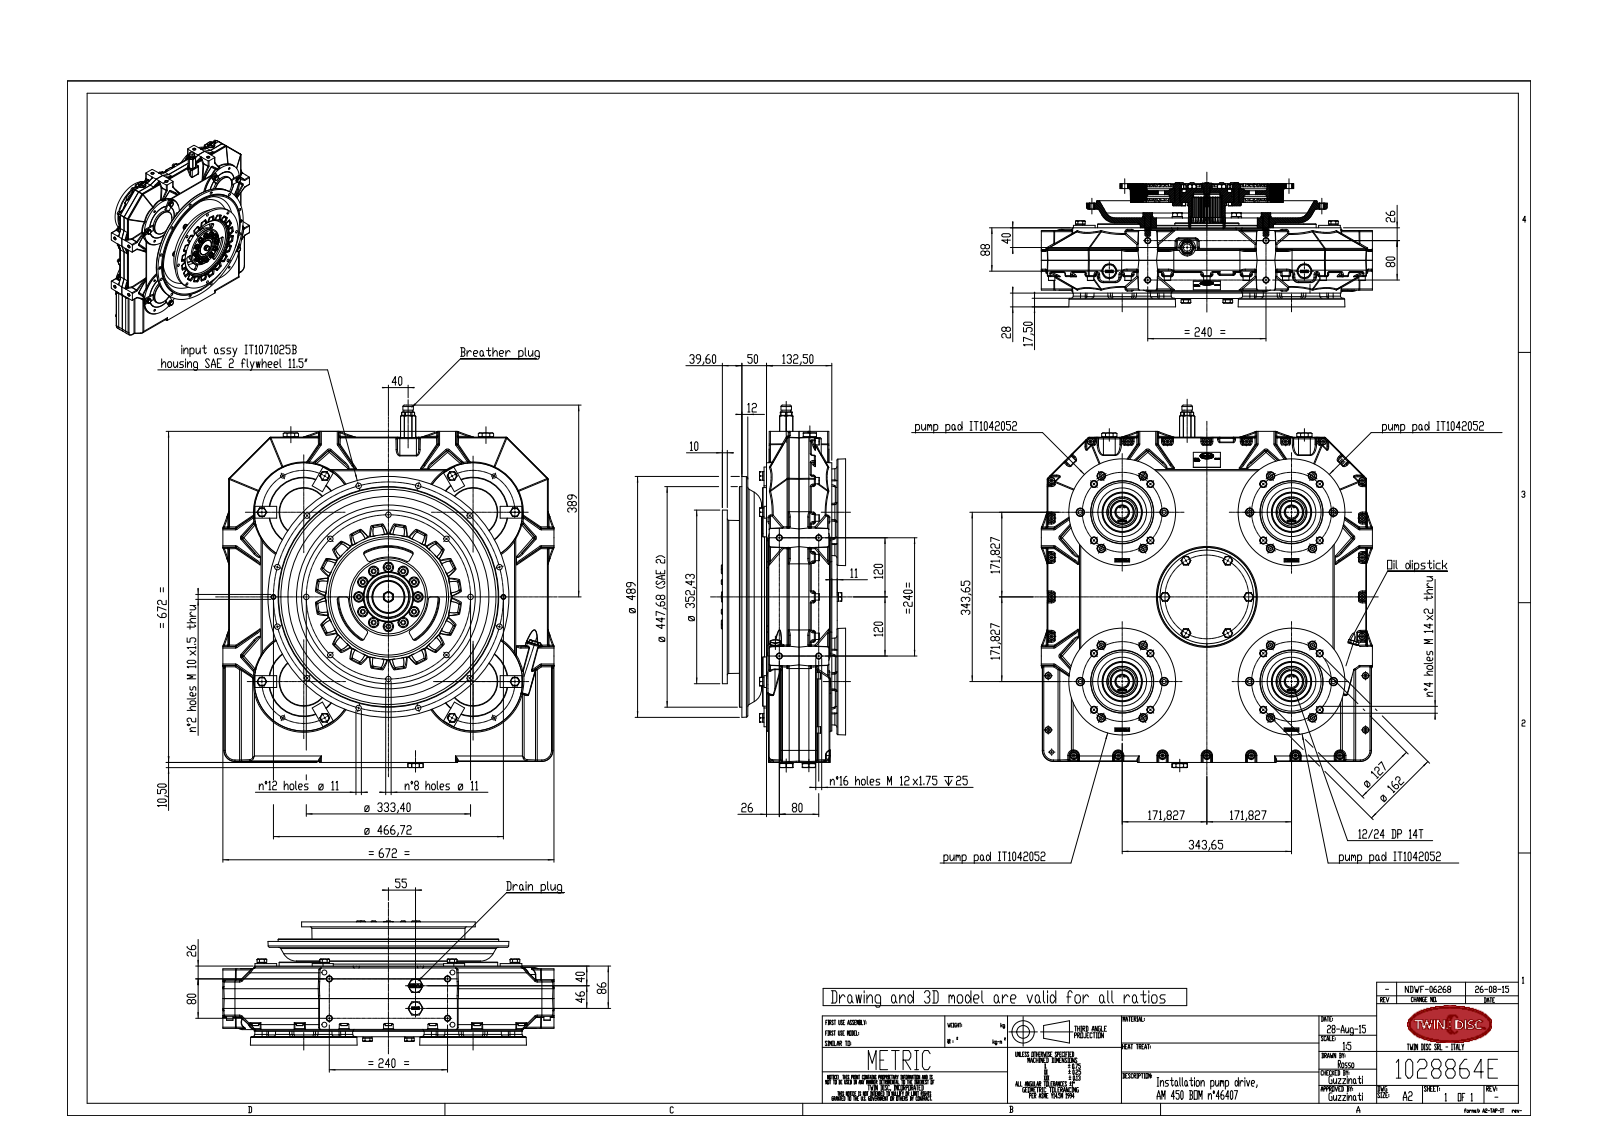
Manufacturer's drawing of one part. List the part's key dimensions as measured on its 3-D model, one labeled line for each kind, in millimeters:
Part name (STEP PRODUCT): IT0000203_rev00-installation; IT4588040_rev00-installation; IT2021216_rev03-installation; ITam450-002_rev00-installation (+7 more)
STEP written by: SolidWorks 2007 (AUTOMOTIVE_DESIGN)
Units: millimetres
Bodies: 62 solids, 12111 faces (4493 planar, 3877 cylindrical, 3741 other)
Overall size (bounding box): 735.8 × 672 × 252.2
Volume: 9 898 000 mm³ · Surface area: 5 049 000 mm²
Round holes (diameter × count): ⌀8.5 ×70, ⌀11 ×42, ⌀10.2 ×29, ⌀12 ×25, ⌀17 ×24, ⌀14 ×17, ⌀10 ×12, ⌀10.5 ×12, ⌀2 ×8, ⌀12.2 ×7, ⌀13 ×7, ⌀16 ×7
Round bosses / shafts (diameter × count): ⌀10 ×44, ⌀13 ×28, ⌀8 ×28, ⌀16.2 ×27, ⌀16 ×24, ⌀18.1 ×14, ⌀21 ×12, ⌀21.1 ×7
Partial cylindrical surfaces — rounded edges, fillets, slot ends (radius × count): R2.5 ×364, R2 ×106, R1 ×84, R4 ×80, R0.45 ×58, R4.5 ×48, R3 ×40, R42.91 ×40
Main face-to-face distances: 128.5, 4, 62.5, 66, 28, 66.5, 124.5, 62, 10, 132.5
Hole centre spacings: 120, 57.4, 75, 138.58, 197.23, 254.31, 300.75, 207.84
